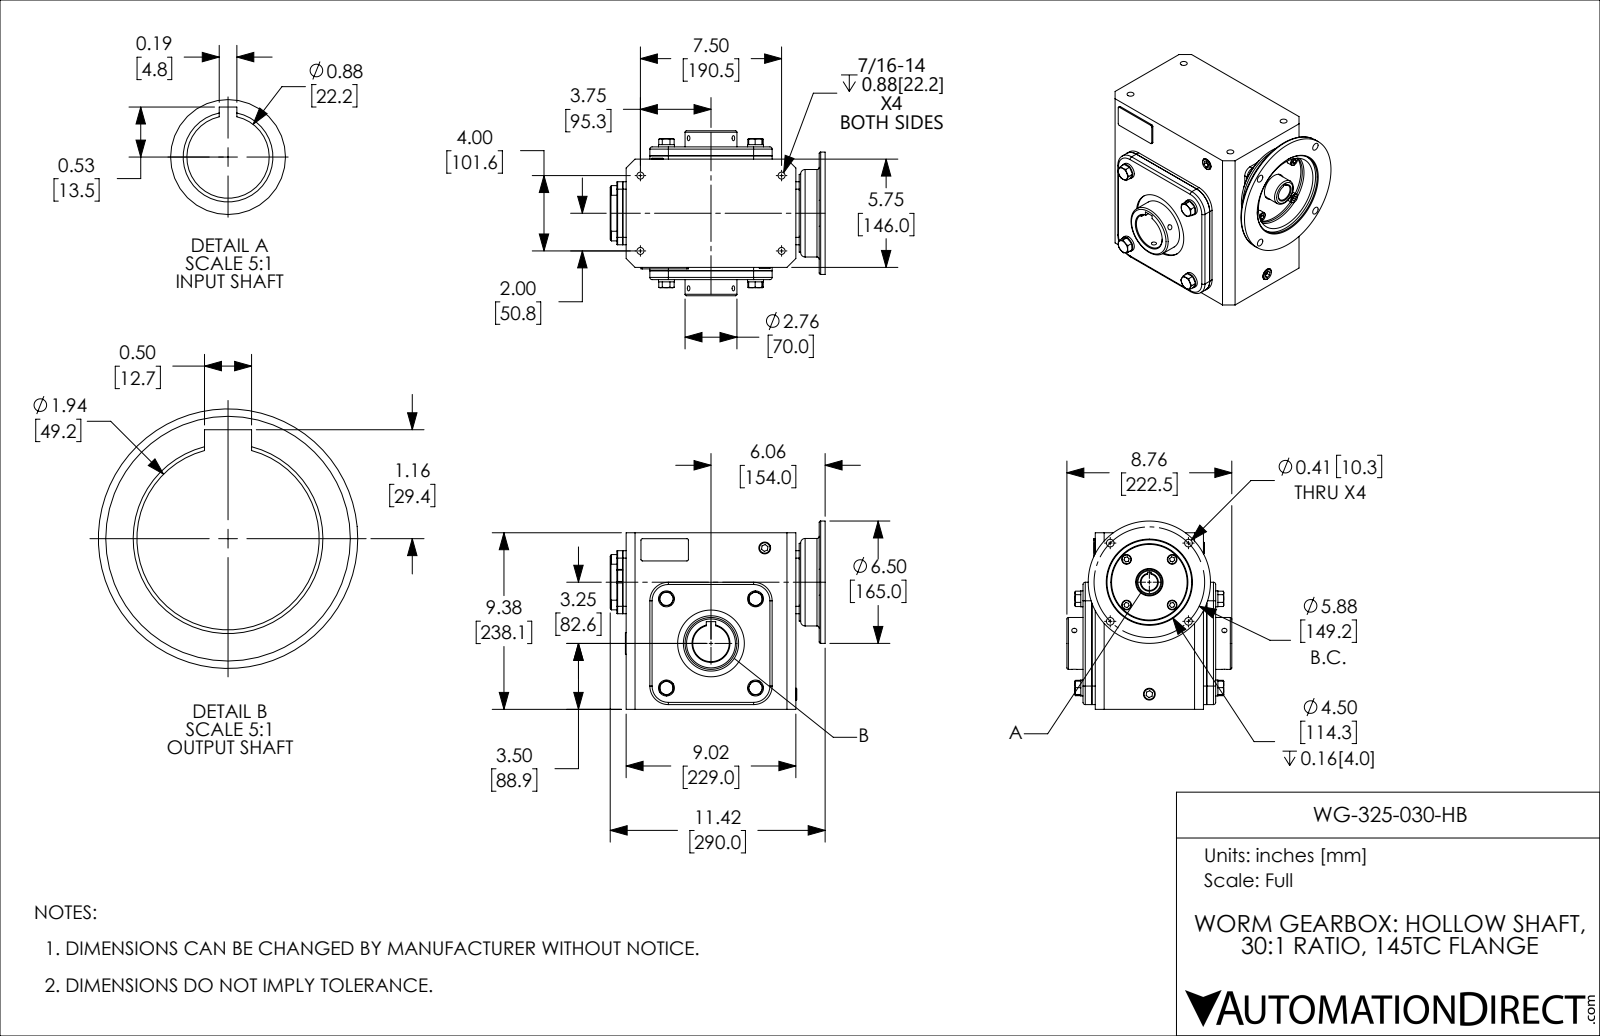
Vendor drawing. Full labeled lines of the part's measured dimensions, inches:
Part name (STEP PRODUCT): WG-325-030-HB
STEP written by: SolidWorks 2017 (AUTOMOTIVE_DESIGN)
Units: inches
Bodies: 39 solids, 587 faces (314 planar, 178 cylindrical, 95 other)
Overall size (bounding box): 11.417 × 9.998 × 8.76
Volume: 516.3 in³ · Surface area: 987.3 in²
Round holes (diameter × count): ⌀0.272 ×6, ⌀0.368 ×4, ⌀0.406 ×4, ⌀0.628 ×3, ⌀0.591 ×1, ⌀0.875 ×1, ⌀0.978 ×1, ⌀1.181 ×1, ⌀1.457 ×1, ⌀1.937 ×1, ⌀2.441 ×1, ⌀2.756 ×1
Round bosses / shafts (diameter × count): ⌀0.846 ×4, ⌀0.512 ×4, ⌀6.496 ×1, ⌀4.646 ×1, ⌀4.134 ×1, ⌀2.835 ×1, ⌀1.378 ×1, ⌀1.142 ×1
Partial cylindrical surfaces — rounded edges, fillets, slot ends (radius × count): R0.118 ×8, R0.079 ×7, R0.394 ×4, R0.906 ×4, R0.984 ×4, R0.02 ×2, R0.039 ×2
Main face-to-face distances: 0.079, 0.177, 6.496, 0.394, 0.571, 6.319, 5.925, 6.398, 0.65, 0.472
Hole centre spacings: 2.937, 4.154, 4.244, 7.064, 7.972, 2.385, 4, 4.389
